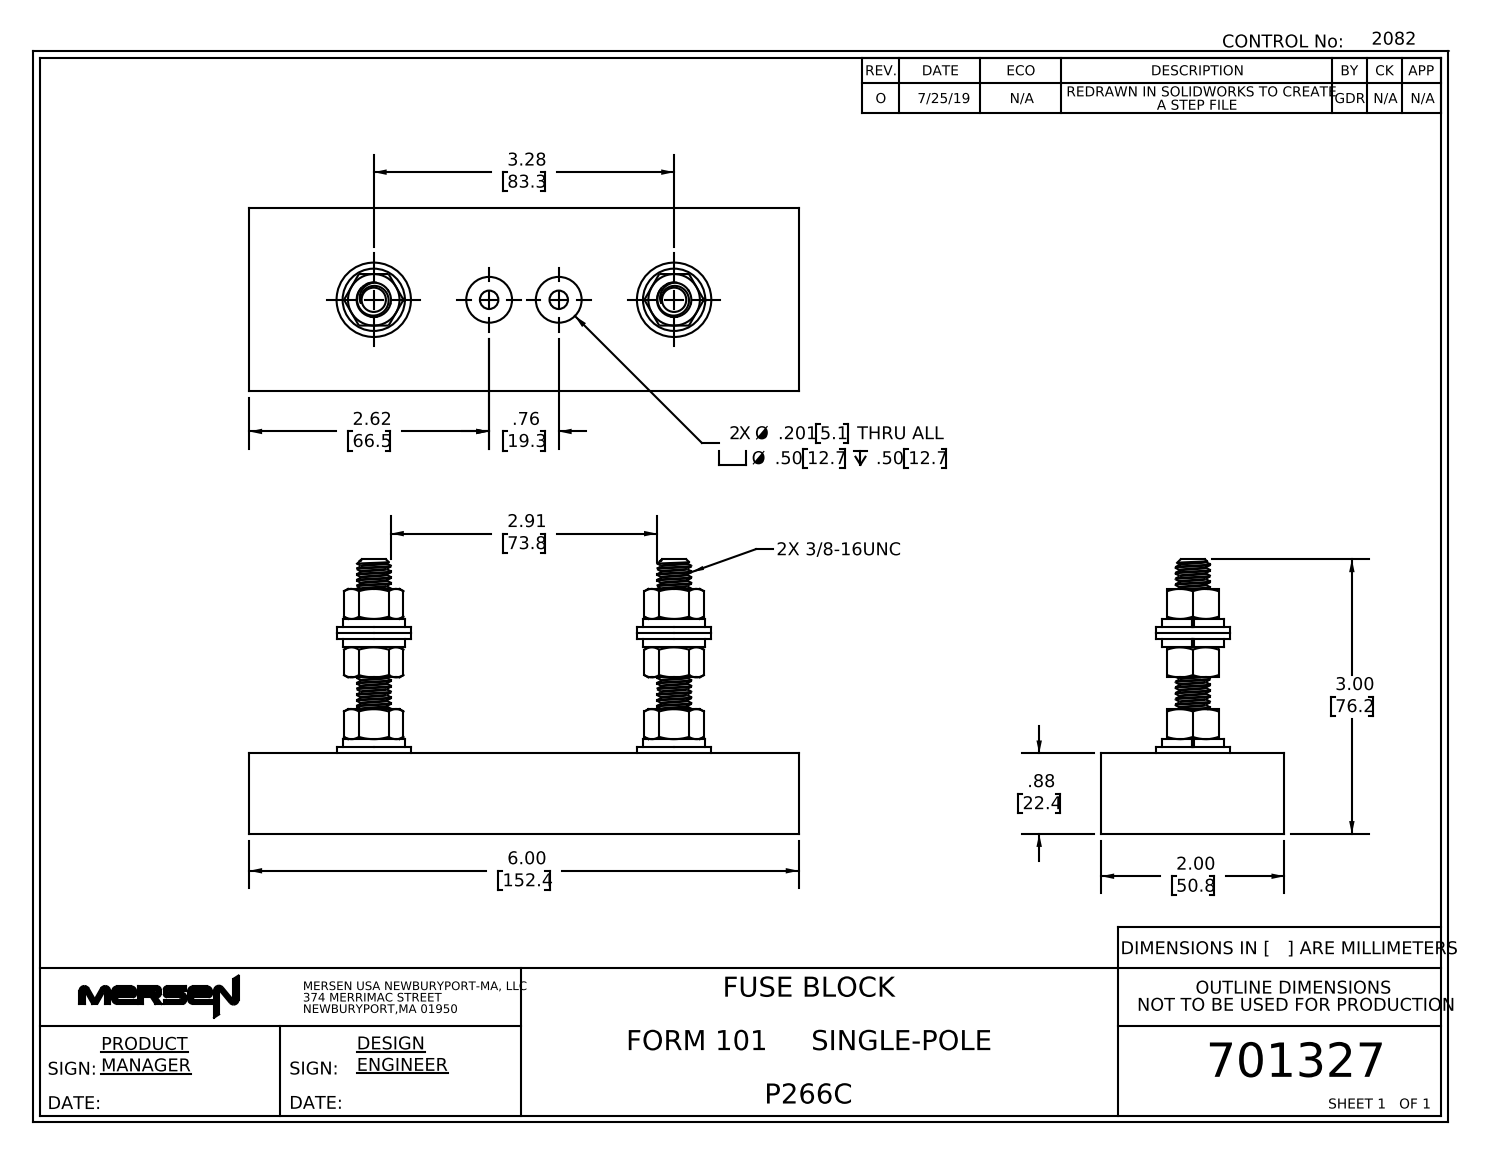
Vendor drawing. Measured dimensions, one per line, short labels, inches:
name: 701327revO
written by: SolidWorks 2017 (AUTOMOTIVE_DESIGN)
unit: in
bodies: 21 solids, 256 faces (98 planar, 46 cylindrical, 112 other)
size: 6 × 3 × 2
volume: 11.31 in³; area: 71.95 in²
holes: 2× ⌀0.201, 2× ⌀0.294, 2× ⌀0.313, 2× ⌀0.375, 2× ⌀0.38, 2× ⌀0.406, 2× ⌀0.5
bosses: 2× ⌀0.812, 2× ⌀0.68, 2× ⌀0.375
face distances: 0.88, 2, 0.065, 1.313, 1.248, 6, 2.193, 0.09, 0.155, 0.22
hole spacings: 1.26, 2.02, 0.76, 3.28
